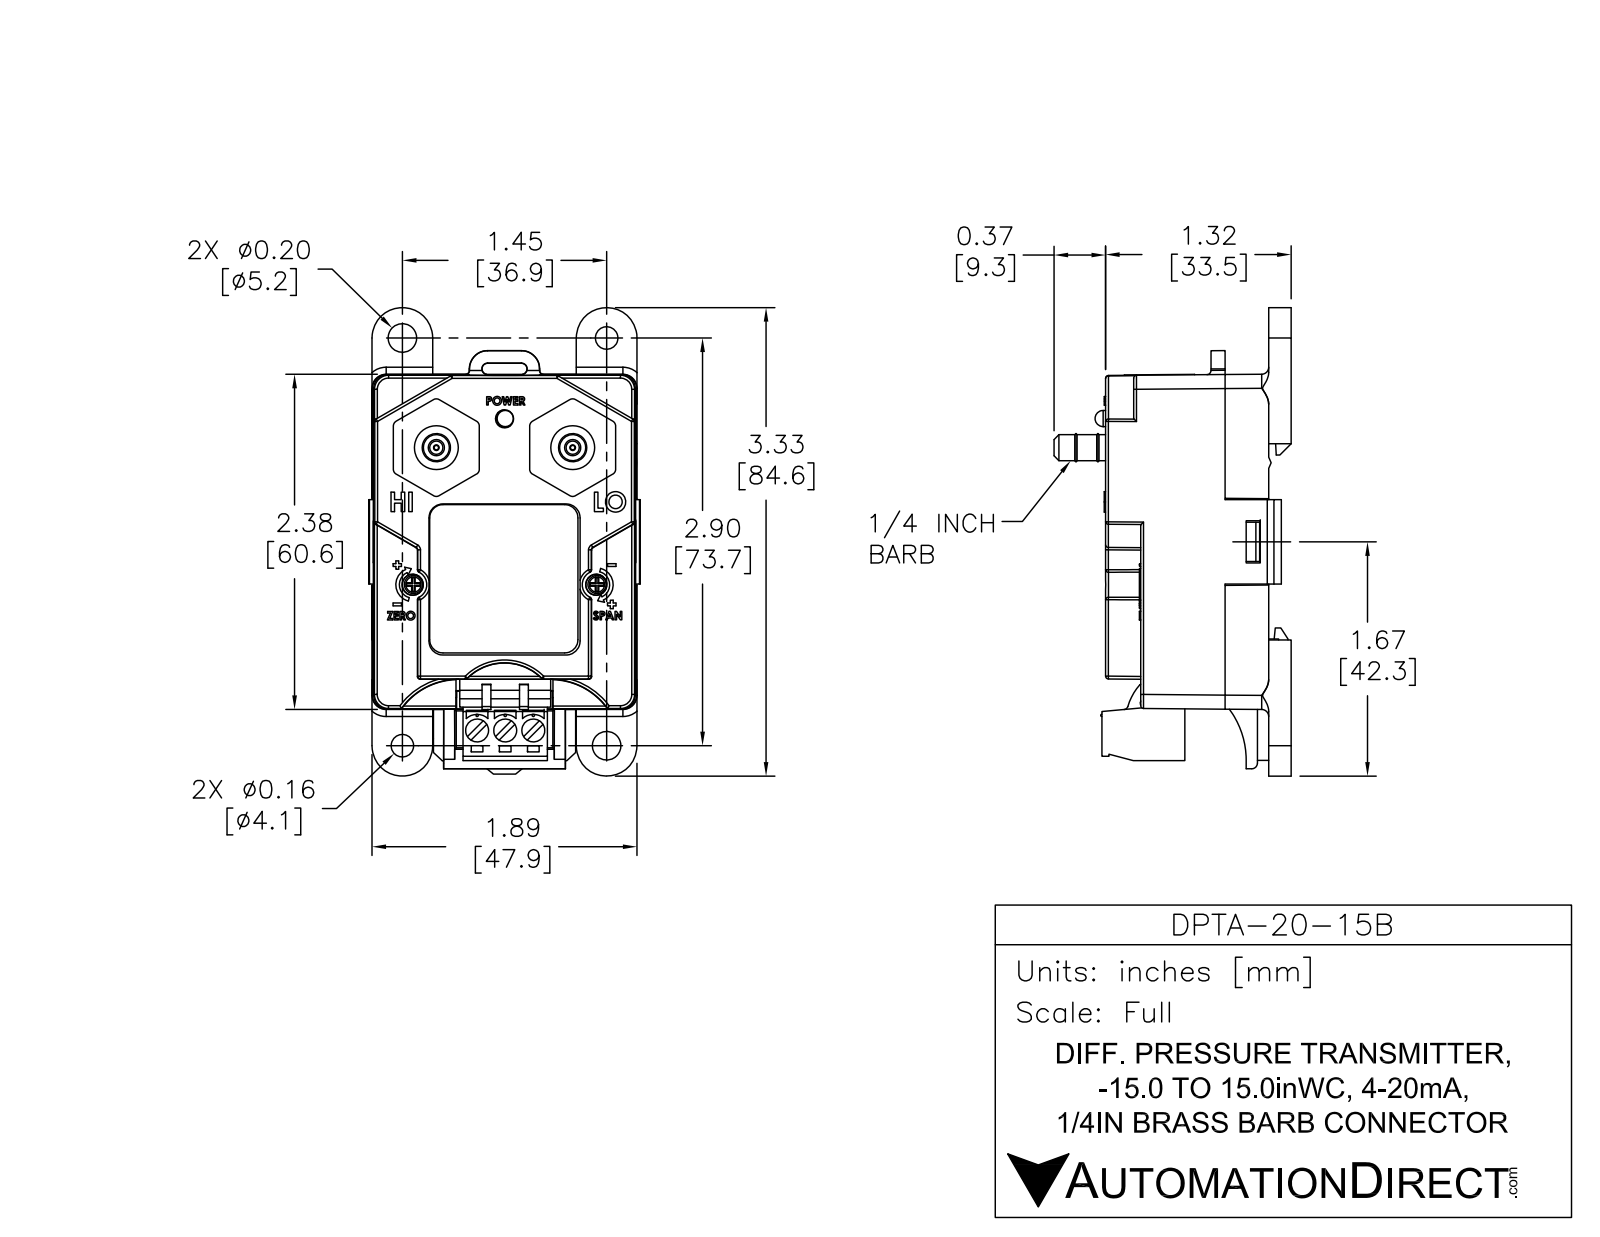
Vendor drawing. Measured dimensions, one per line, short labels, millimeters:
name: DPTA-20-15B
written by: SolidWorks 2011 (AUTOMOTIVE_DESIGN)
unit: mm
bodies: 11 solids, 448 faces (354 planar, 85 cylindrical, 9 other)
size: 85.01 × 49.76 × 43.1
volume: 29 684 mm³; area: 34 743 mm²
holes: 7× ⌀4, 2× ⌀2.5, 2× ⌀5.12, 1× ⌀3.1
bosses: 3× ⌀5, 3× ⌀3.5, 3× ⌀3.5, 2× ⌀8, 2× ⌀4.75, 1× ⌀3
rounds: 12× R3, 4× R2, 4× R5.5, 2× R0.99, 2× R1.06, 2× R1.12, 2× R2.38, 2× R3.25
face distances: 1, 1.9, 4, 29.1, 0.5, 46.9, 5.9, 5, 33.1, 27.2
hole spacings: 13.55, 20.73, 23.37, 24.92, 29.43, 34.46, 36.67, 38.22
